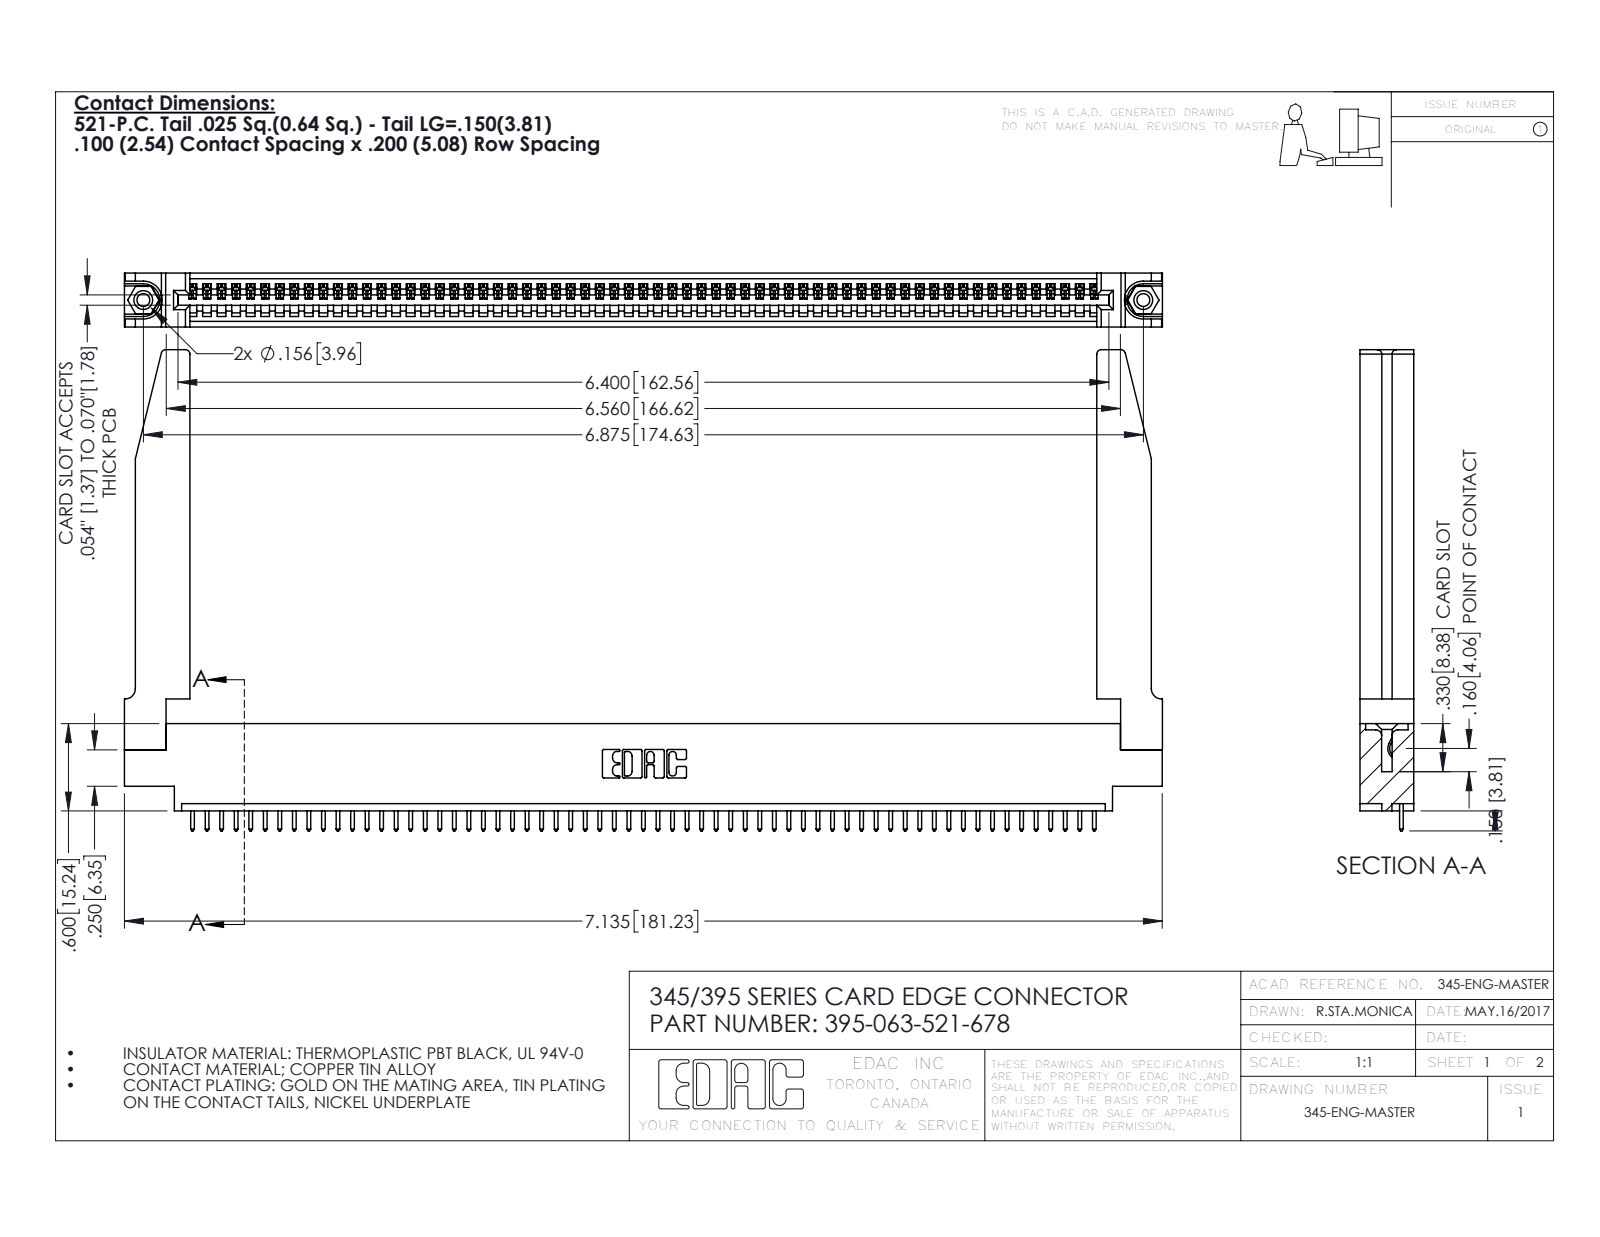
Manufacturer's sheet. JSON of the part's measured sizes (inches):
{"part_name": "345-220-078_345-220-078; 345-250-001_345-250-001-102; 395-063-521-678; 345-292-001_345-293-121 (+1 more)", "step_written_by": "SolidWorks 2016 (CONFIG_CONTROL_DESIGN)", "units": "inches", "bodies": {"solids": 68, "faces": 4018, "planar": 2746, "cylindrical": 1220, "other": 52}, "overall_size": [7.136, 3.307, 0.37], "volume_in3": 1.517, "surface_area_in2": 45.38, "round_holes": [[0.089, 2], [0.125, 2], [0.156, 2], [0.064, 1]], "round_bosses_or_shafts": [[0.155, 2]], "partial_cylinders_radius": [[0.006, 126], [0.01, 126], [0.01, 22], [0.03, 8], [0.007, 6], [0.031, 6], [0.026, 3], [0.031, 2]], "face_to_face_distances": [0.37, 0.072, 0.298, 0.098, 0.272, 0.025, 0.2, 0.225, 0.148, 0.15], "hole_center_spacings": [0.27, 6.639, 6.875]}
